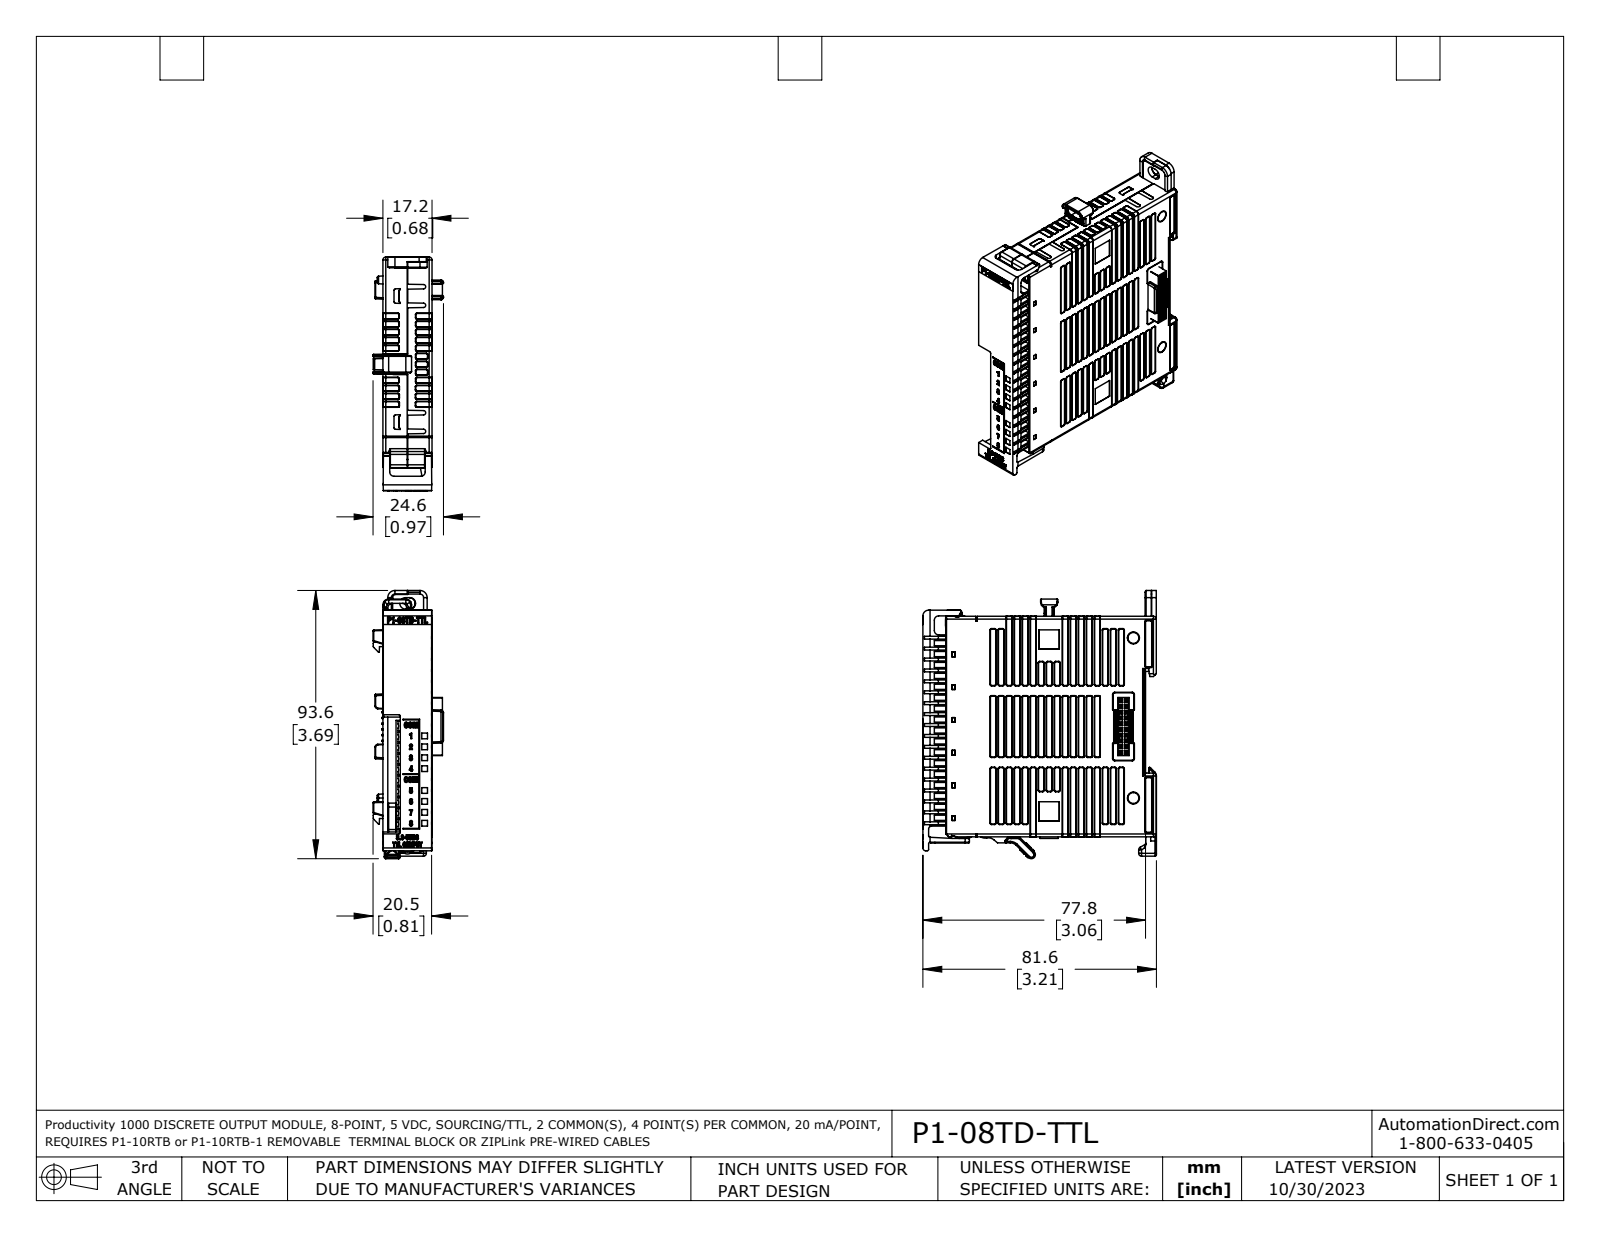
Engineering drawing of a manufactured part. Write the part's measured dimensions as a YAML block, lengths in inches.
part_name: "P1-04ADL-1 Coord 1 WO Face nc ext2Bcc BODY W P1-08TD-TTL face WO CAP SEPERATED 1 DIN Coord sr1 fxt"
step_written_by: "SolidWorks 2021 (AUTOMOTIVE_DESIGN)"
units: inches
bodies: {solids: 6, faces: 4546, planar: 2440, cylindrical: 1039, other: 1067}
overall_size: [3.686, 3.212, 0.969]
volume: 5.542
surface_area: 46.51
round_holes:
  - {diameter: 0.01, count: 20}
  - {diameter: 0.024, count: 8}
  - {diameter: 0.049, count: 1}
round_bosses_or_shafts:
  - {diameter: 0.043, count: 2}
partial_cylinders:
  - {radius: 0.01, count: 207}
  - {radius: 0.02, count: 139}
  - {radius: 0.039, count: 58}
  - {radius: 0.079, count: 12}
  - {radius: 0.059, count: 11}
  - {radius: 0.059, count: 10}
  - {radius: 0.008, count: 8}
  - {radius: 0.03, count: 8}
face_to_face_distances: [0.674, 0.675, 0.079, 0.672, 0.315, 2.746, 3.061, 0.236, 0.071, 0.157]
hole_center_spacings: [0.079, 0.157, 0.176, 0.236, 0.315, 0.394, 0.402, 0.111]
